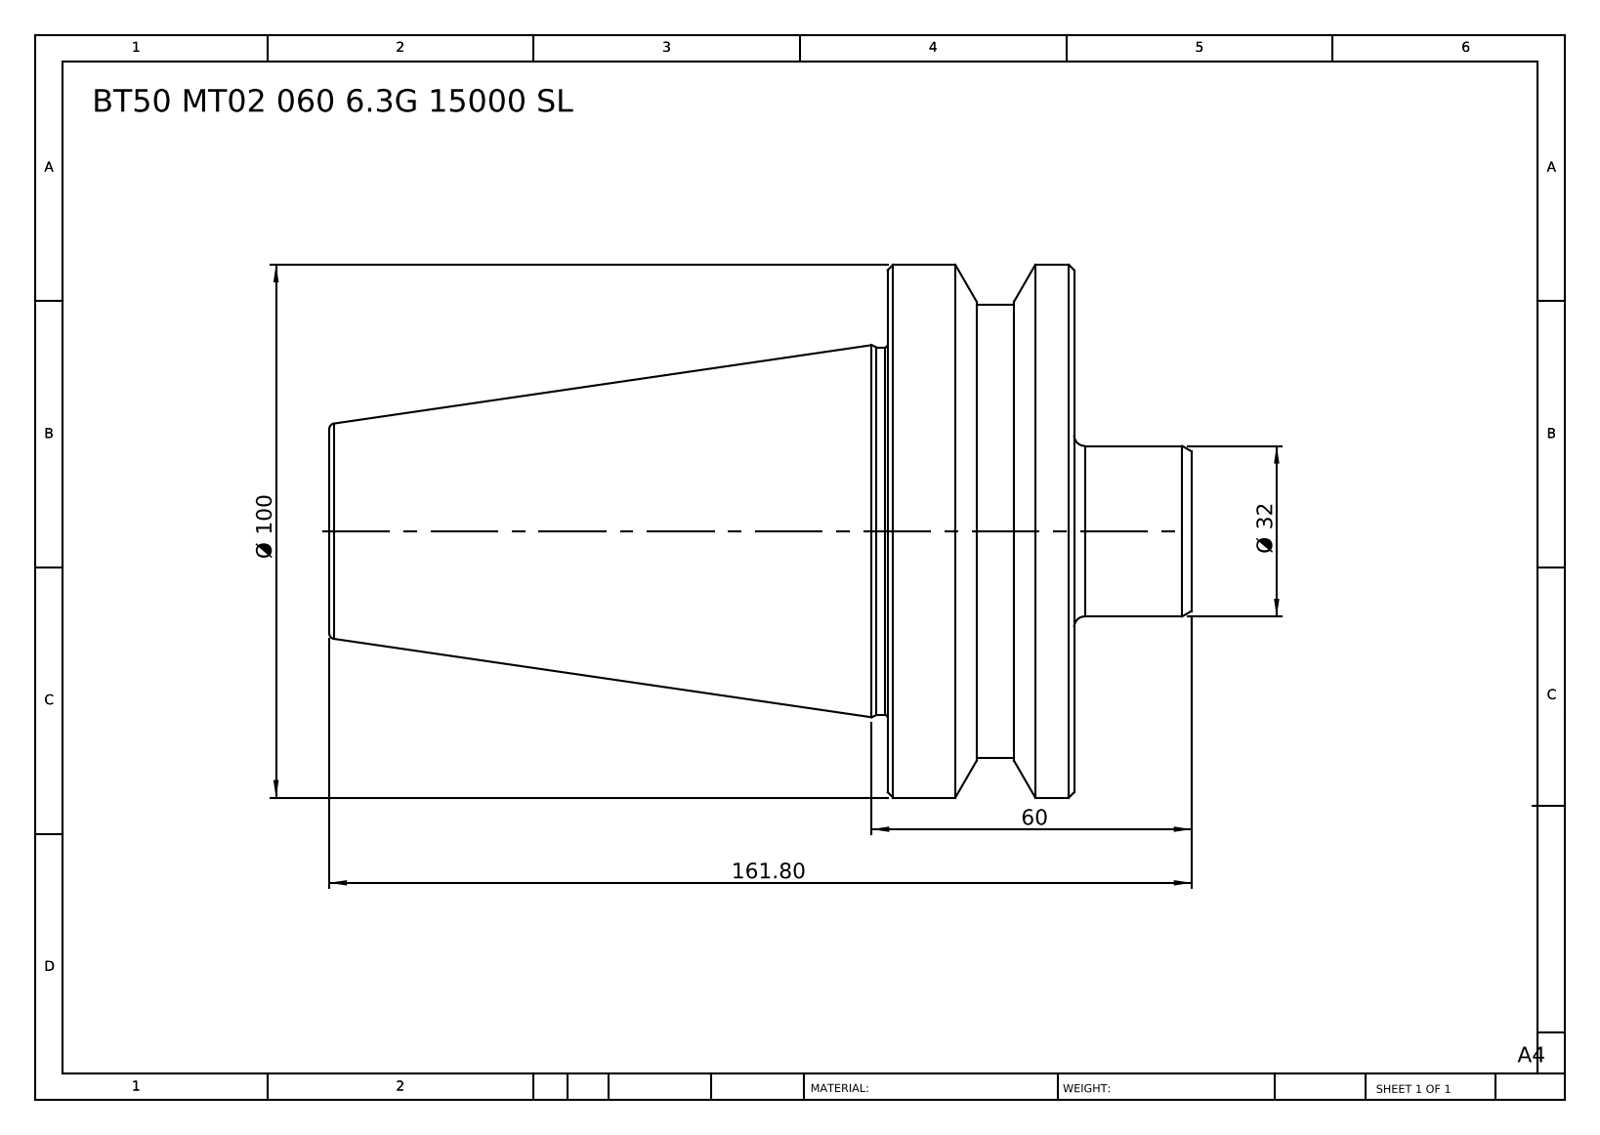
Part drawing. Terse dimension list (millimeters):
name: BT50 MT02 060 6.3G 15000 SL
written by: SolidWorks 2014 (CONFIG_CONTROL_DESIGN)
unit: mm
bodies: 1 solid, 36 faces (6 planar, 10 cylindrical, 20 other)
size: 161.8 × 100 × 100
volume: 527 736 mm³; area: 46 417 mm²
bosses: 1× ⌀100, 1× ⌀85, 1× ⌀69, 1× ⌀32
face distances: 35, 139.8, 104.8, 22, 57, 161.8, 40.3, 18.3, 16.7, 121.5
